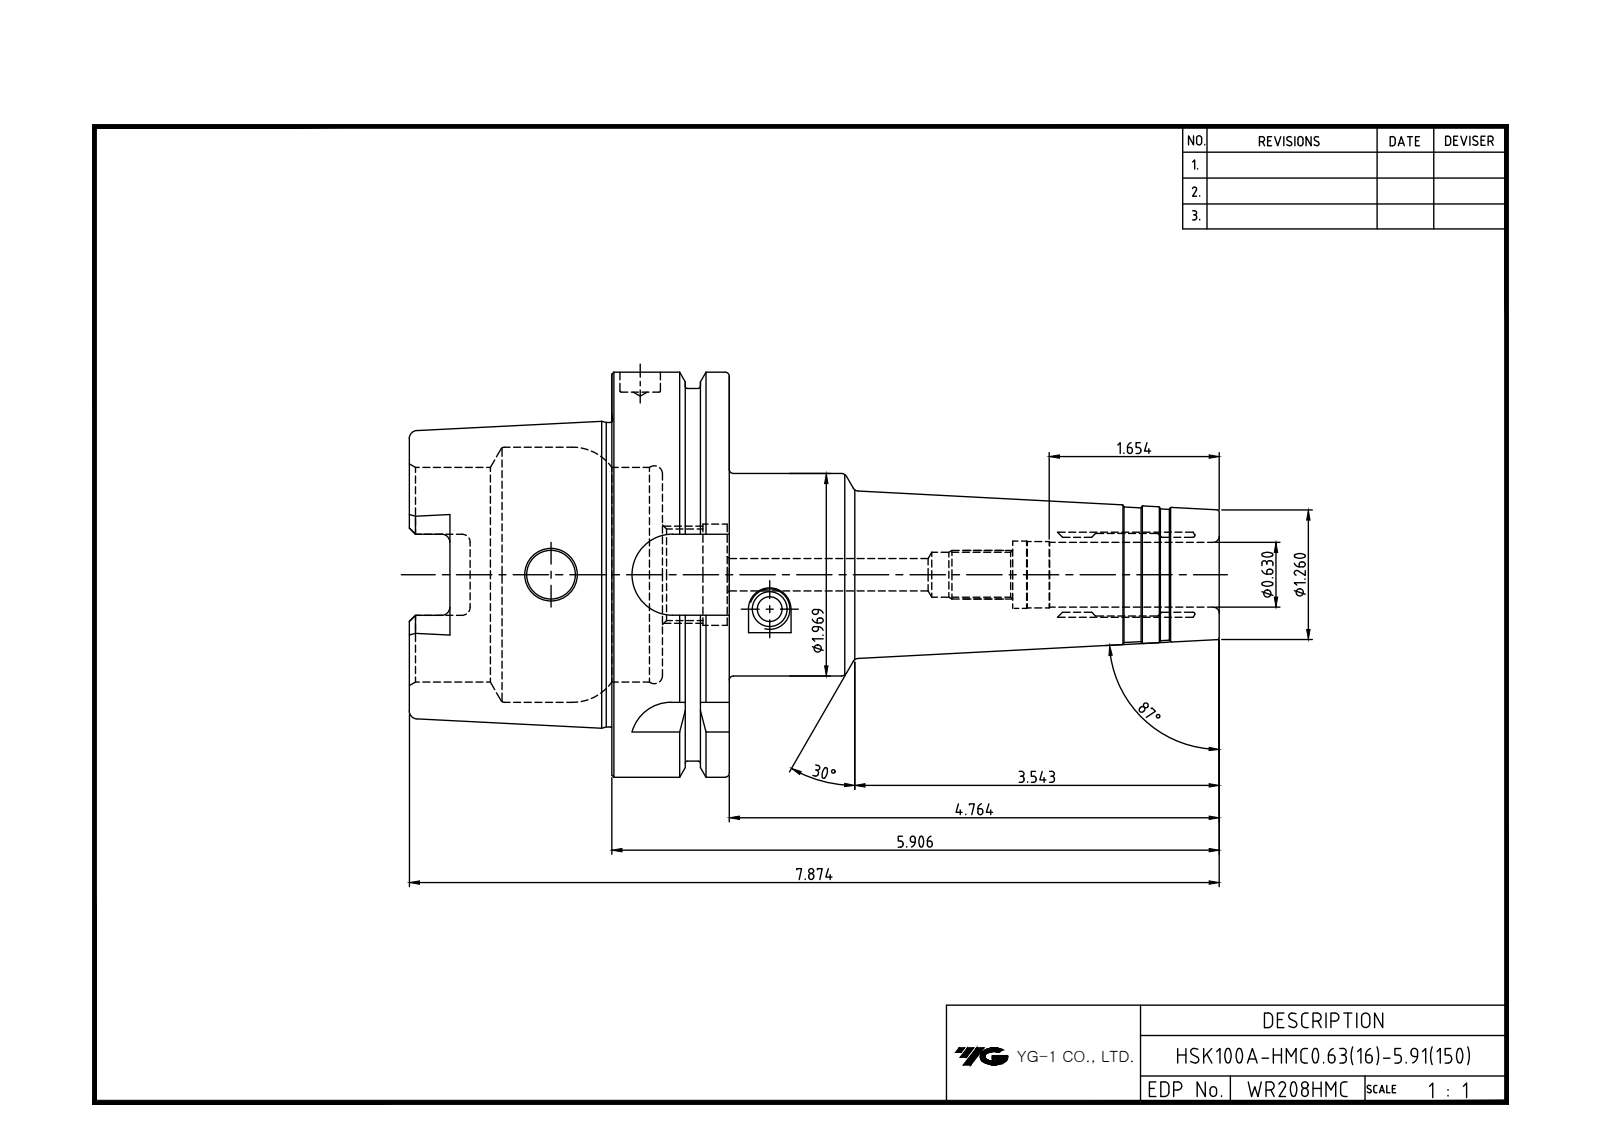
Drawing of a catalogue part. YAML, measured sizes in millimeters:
part_name: "LO-HSK100A-HMC16-150"
step_written_by: "Autodesk Inventor 2025 (AUTOMOTIVE_DESIGN)"
units: millimeters
bodies: {solids: 1, faces: 135, planar: 38, cylindrical: 35, other: 62}
overall_size: [200, 100, 100]
volume: 395005
surface_area: 68482
round_holes:
  - {diameter: 8, count: 1}
  - {diameter: 10, count: 1}
  - {diameter: 10.92, count: 1}
  - {diameter: 12, count: 1}
  - {diameter: 16, count: 1}
  - {diameter: 16.6, count: 1}
  - {diameter: 22.38, count: 1}
  - {diameter: 25, count: 1}
  - {diameter: 53, count: 1}
  - {diameter: 63, count: 1}
round_bosses_or_shafts:
  - {diameter: 100, count: 1}
  - {diameter: 92, count: 1}
  - {diameter: 75.41, count: 1}
  - {diameter: 50, count: 1}
partial_cylinders:
  - {radius: 2, count: 6}
  - {radius: 4.88, count: 4}
  - {radius: 10, count: 4}
face_to_face_distances: [29, 12.5, 16.5, 62.5, 50, 79, 200, 150, 137.5, 121]
